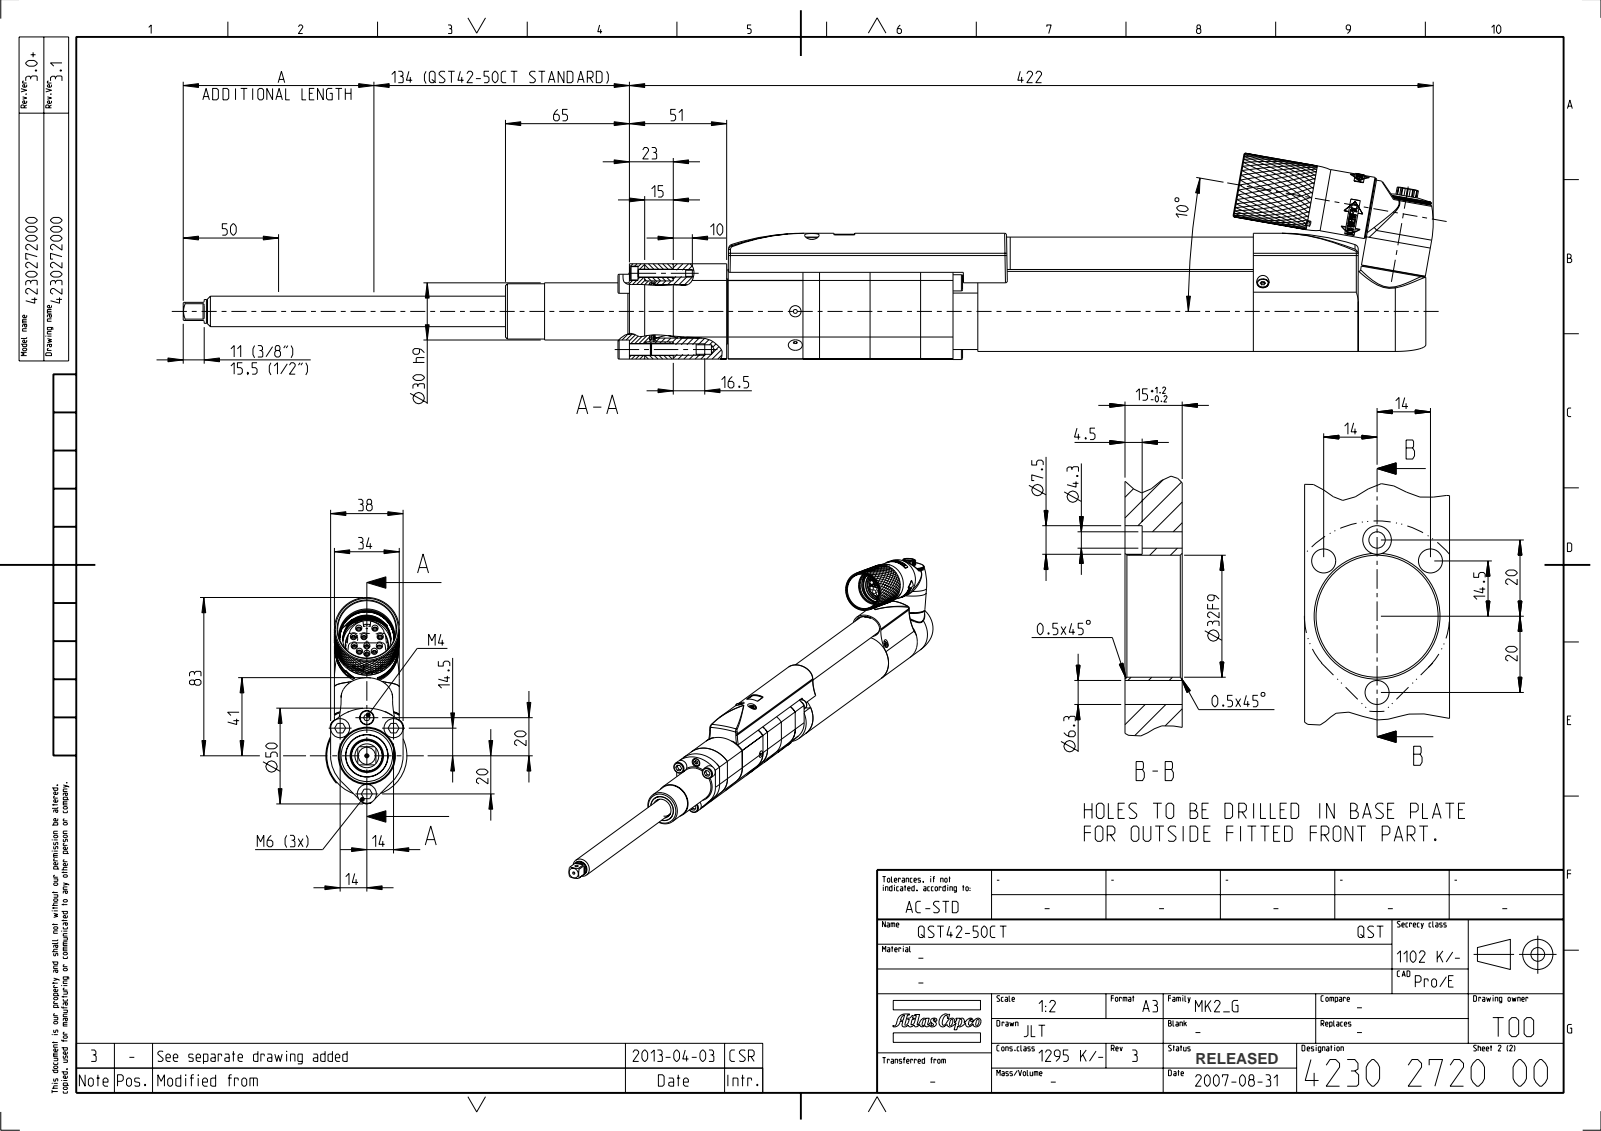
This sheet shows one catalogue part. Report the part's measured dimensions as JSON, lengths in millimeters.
{"part_name": "QST_CONNECTOR_02; QST42_REARCOVER_02; QST42_50_CT_BODY_50; QST42_SPACER_01 (+3 more)", "step_written_by": "PRO/ENGINEER BY PARAMETRIC TECHNOLOGY CORPORATION, 2012420 (CONFIG_CONTROL_DESIGN)", "units": "millimeters", "bodies": {"solids": 8, "faces": 3449, "planar": 1368, "cylindrical": 1115, "other": 966}, "overall_size": [547.15, 166.54, 42], "volume_mm3": 427434, "surface_area_mm2": 239939, "round_holes": [[3.3, 6], [6.3, 6], [3.24, 5], [2.46, 4], [4.3, 4], [5, 4], [1.4, 3], [2.94, 3], [3.5, 3], [4.13, 3], [5.5, 3], [7.3, 3]], "round_bosses_or_shafts": [[3, 7], [6, 6], [4, 6], [2.5, 5], [5, 4], [34, 3], [10, 3], [8.5, 3]], "partial_cylinders_radius": [[0.5, 23], [0.2, 10], [1, 9], [1.5, 6], [2, 5], [0.6, 4], [5.25, 4], [40, 4]], "face_to_face_distances": [38, 3.5, 15, 5.78, 409.8, 394.8, 406.3, 391.3, 9, 216.25], "hole_center_spacings": [14.97, 16.7, 14.98, 15.01, 15, 15.02, 15.03, 20.23]}
